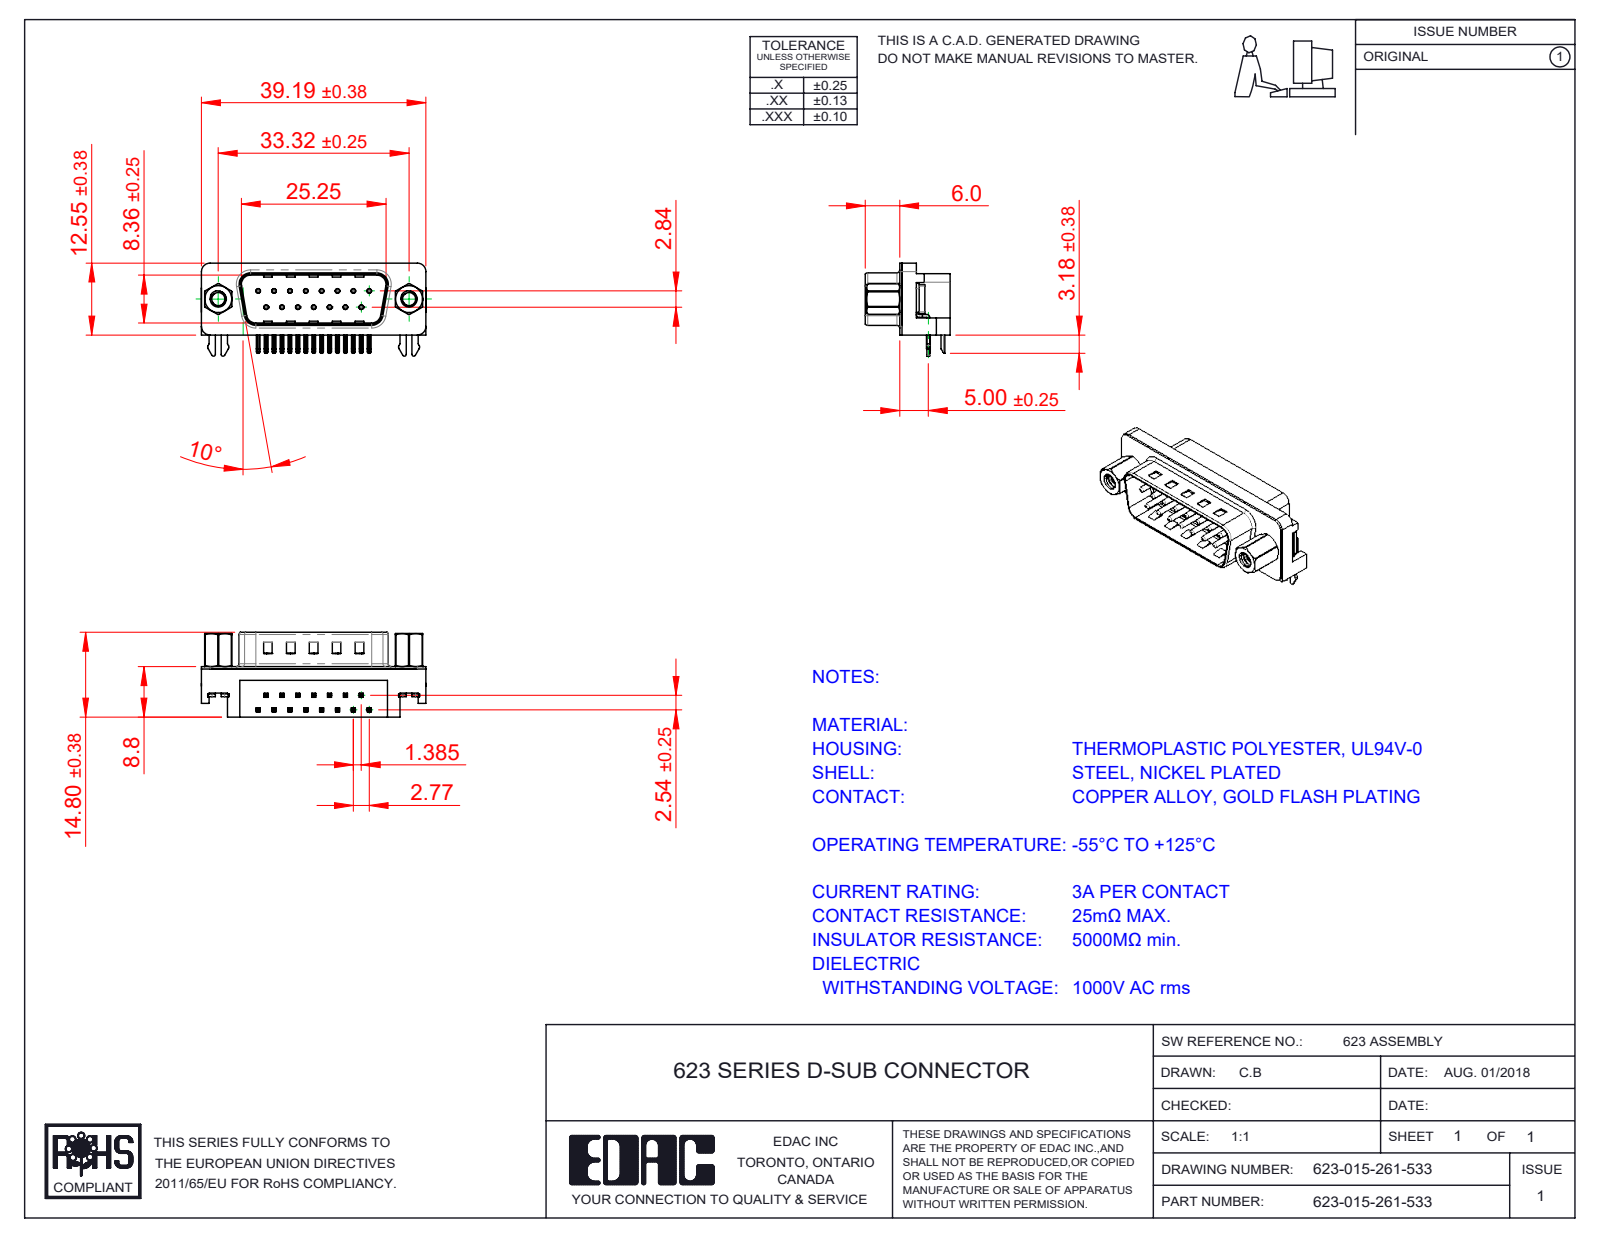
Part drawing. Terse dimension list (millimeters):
name: 623-015-261-533; 623 4-40 Threaded Rivet; 623 Shell_15 Socket; 623 Housing_15 Socket (+4 more)
written by: SolidWorks 2016 (CONFIG_CONTROL_DESIGN)
unit: mm
bodies: 23 solids, 1623 faces (943 planar, 507 cylindrical, 173 other)
size: 39.22 × 16.25 × 14.8
volume: 3 536 mm³; area: 5 417 mm²
holes: 15× ⌀0.35, 15× ⌀0.8, 2× ⌀2.26, 2× ⌀2.29, 2× ⌀4, 2× ⌀4.8, 2× ⌀5
bosses: 15× ⌀0.75, 2× ⌀4.9, 2× ⌀4.75, 2× ⌀3.9, 2× ⌀2.79
rounds: 68× R0.25, 30× R0.12, 14× R0.5, 8× R1, 6× R1.5, 4× R0.32, 4× R0.9, 4× R1.6
face distances: 0.4, 8.4, 8.8, 2.1, 1.7, 10.46, 10.86, 8.76, 5.9, 2.9
hole spacings: 3.16, 2.77, 5.54, 8.31, 11.08, 5.03, 5.04, 7.48
